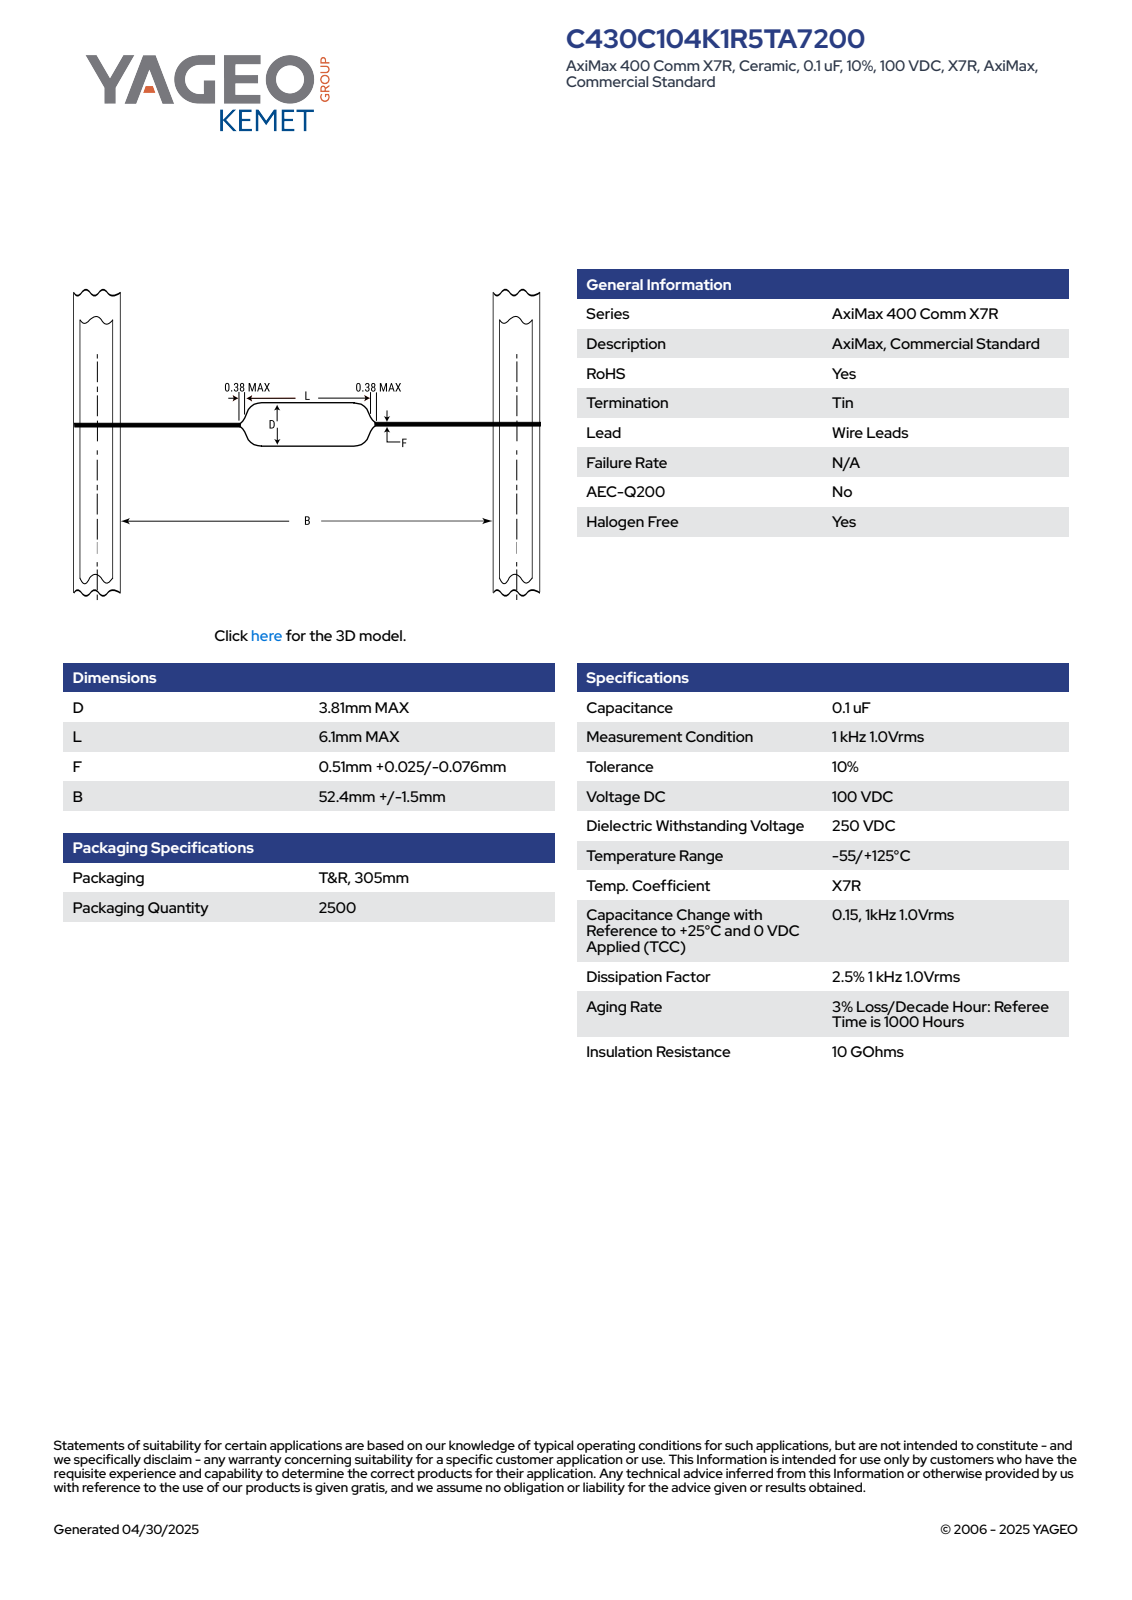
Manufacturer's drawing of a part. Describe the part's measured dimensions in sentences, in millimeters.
The part is named "CCA_ACSTTAPE_C430_D3.81L6.1LL25.4F0.535". Its 3-D file was written by "SolidWorks 2014 (AUTOMOTIVE_DESIGN)". It is 1 solid with 74 faces: 26 planar, 9 cylindrical and 39 other. Overall it measures 56.44 by 3.81 by 3.81 millimeters. Its volume is 78 cubic millimeters and its surface area 172 square millimeters. Round bosses or shafts: 1 of diameter 3.81, 1 of diameter 0.54. Partial cylindrical surfaces (rounded edges, fillets, slot ends): 1 of radius 1.9. The main face-to-face distances are 6.1, 24.79, 30.89, 56.44, 31.65, 25.55.
